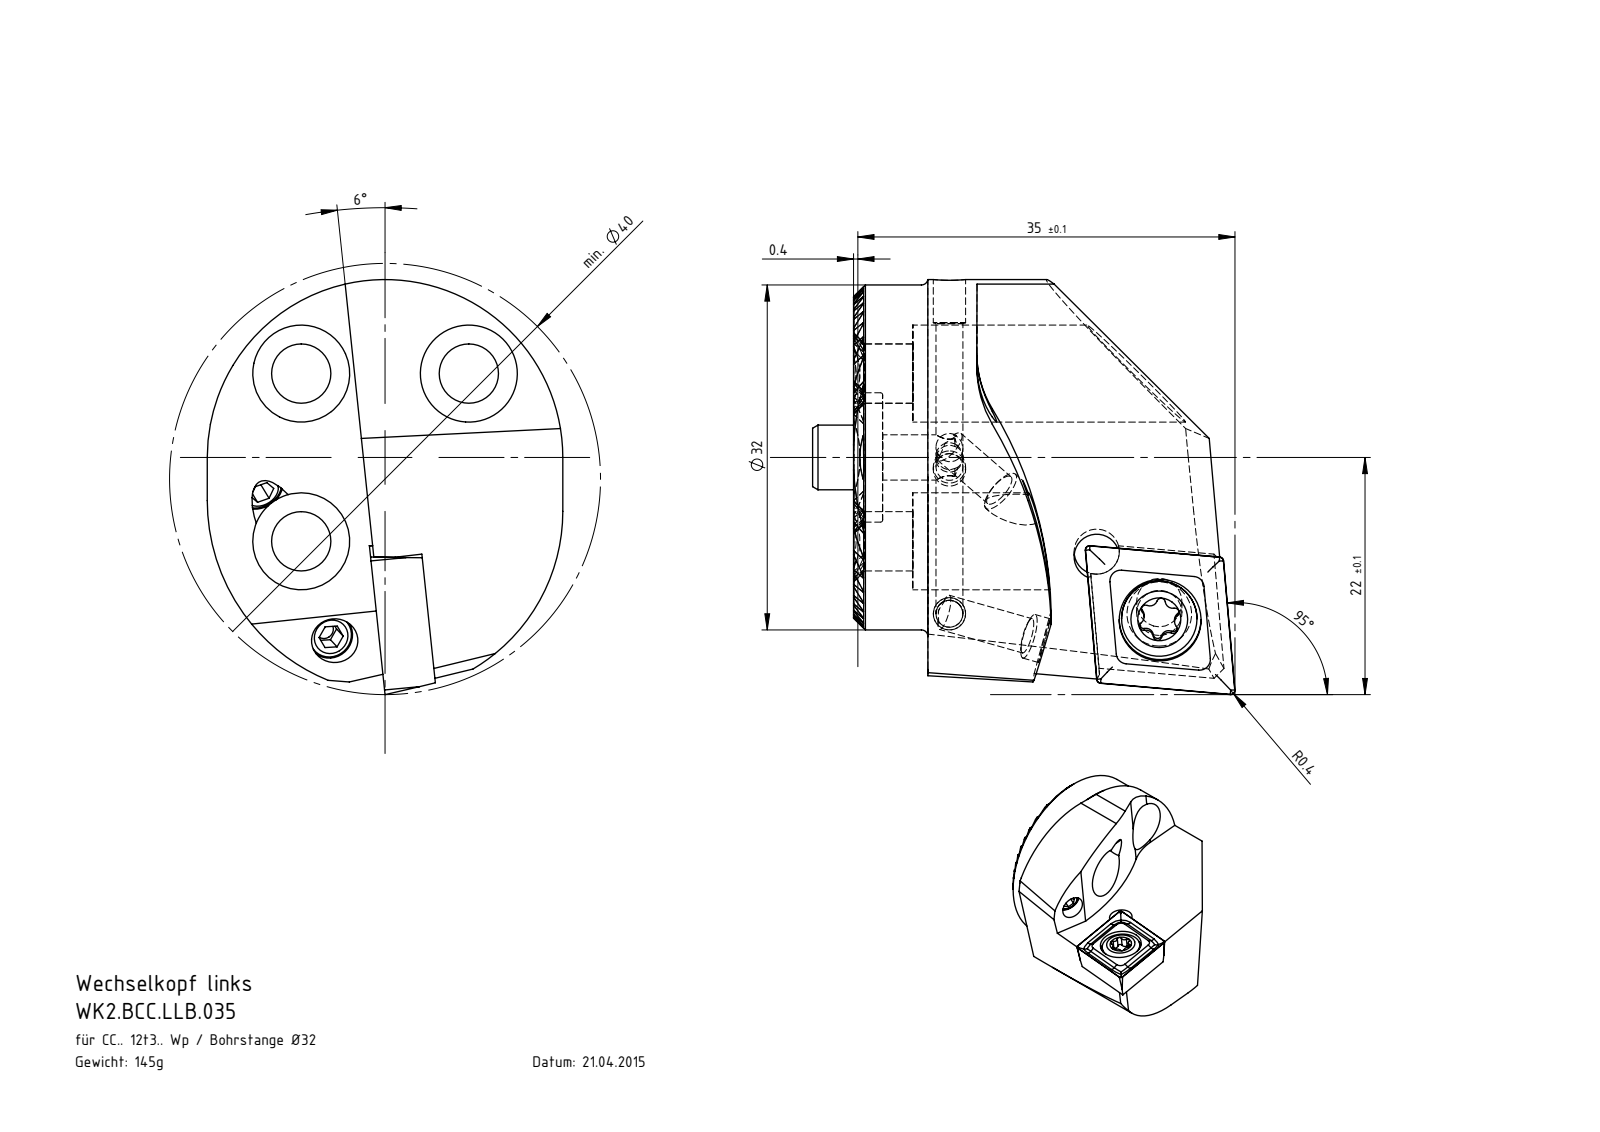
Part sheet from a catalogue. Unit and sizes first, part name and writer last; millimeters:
Units: millimetres
Overall size (bounding box): 39.2 × 38.5 × 33
Round holes (diameter × count): ⌀4.2 ×5, ⌀5.5 ×4, ⌀2.38 ×3, ⌀2.5 ×3, ⌀9 ×3, ⌀1.7 ×2, ⌀3.3 ×2, ⌀3 ×1, ⌀7.6 ×1, ⌀12 ×1
Round bosses / shafts (diameter × count): ⌀3 ×3, ⌀4 ×2, ⌀32 ×1, ⌀7 ×1, ⌀6 ×1, ⌀5 ×1
Partial cylindrical surfaces — rounded edges, fillets, slot ends (radius × count): R0.12 ×22, R0.39 ×6, R0.69 ×3, R0.69 ×3, R10 ×1, R16.5 ×1, R17 ×1, R18 ×1
Main face-to-face distances: 1.3, 2.6, 3.9, 5.2, 6.5, 12.99, 11.69, 14.29, 7.8, 10.39
Hole centre spacings: 11, 15.56, 8.2, 8.32, 22.01
Volume: 18 470 mm³ · Surface area: 9 143 mm²
Bodies: 12 solids, 561 faces (191 planar, 194 cylindrical, 176 other)
Part name (STEP PRODUCT): CCMT120404; WK2-BCC.LLB.035_A; WCC-ER2.001.010_A; WK2-ER1.001.012_A_Fertigbearbeitung (+3 more)
STEP written by: SolidWorks 2017 (AUTOMOTIVE_DESIGN)
